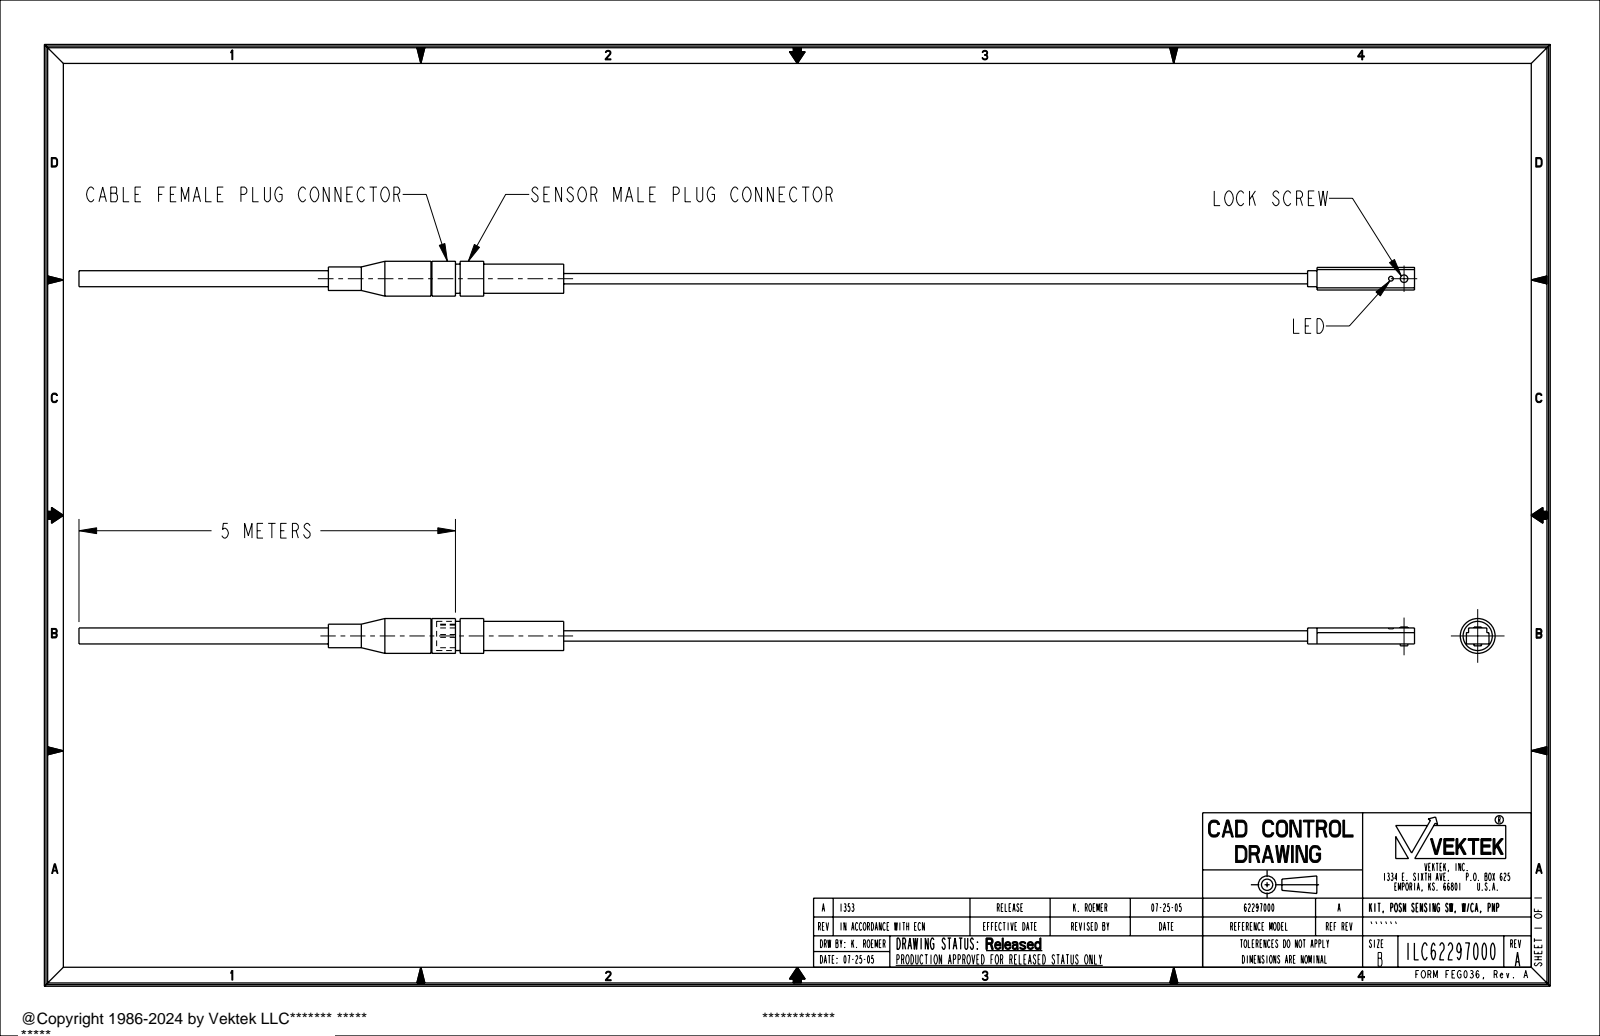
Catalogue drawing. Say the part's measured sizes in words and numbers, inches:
The part is named "ILC62297000_29700100; ILC62297000_27642400; ILC62297000_ASM". Its 3-D file was written by "PRO/ENGINEER BY PARAMETRIC TECHNOLOGY CORPORATION, 2004290 (AUTOMOTIVE_DESIGN_CC2)". It is 2 solids with 79 faces: 33 planar, 44 cylindrical and 2 other. Overall it measures 14.19 by 0.37 by 0.37 inches. Its volume is 0.389 cubic inches and its surface area 8.891 square inches. Round holes: 3 of diameter 0.03, 1 of diameter 0.05. Round bosses or shafts: 1 of diameter 0.37, 1 of diameter 0.35, 1 of diameter 0.31, 1 of diameter 0.25, 1 of diameter 0.17, 1 of diameter 0.11, 1 of diameter 0.08. The main face-to-face distances are 0.17, 0.24, 0.023, 0.217, 1.15, 0.05, 1.35, 0.25, 0.2, 0.194. The hole center spacings are 0.141, 0.2.
